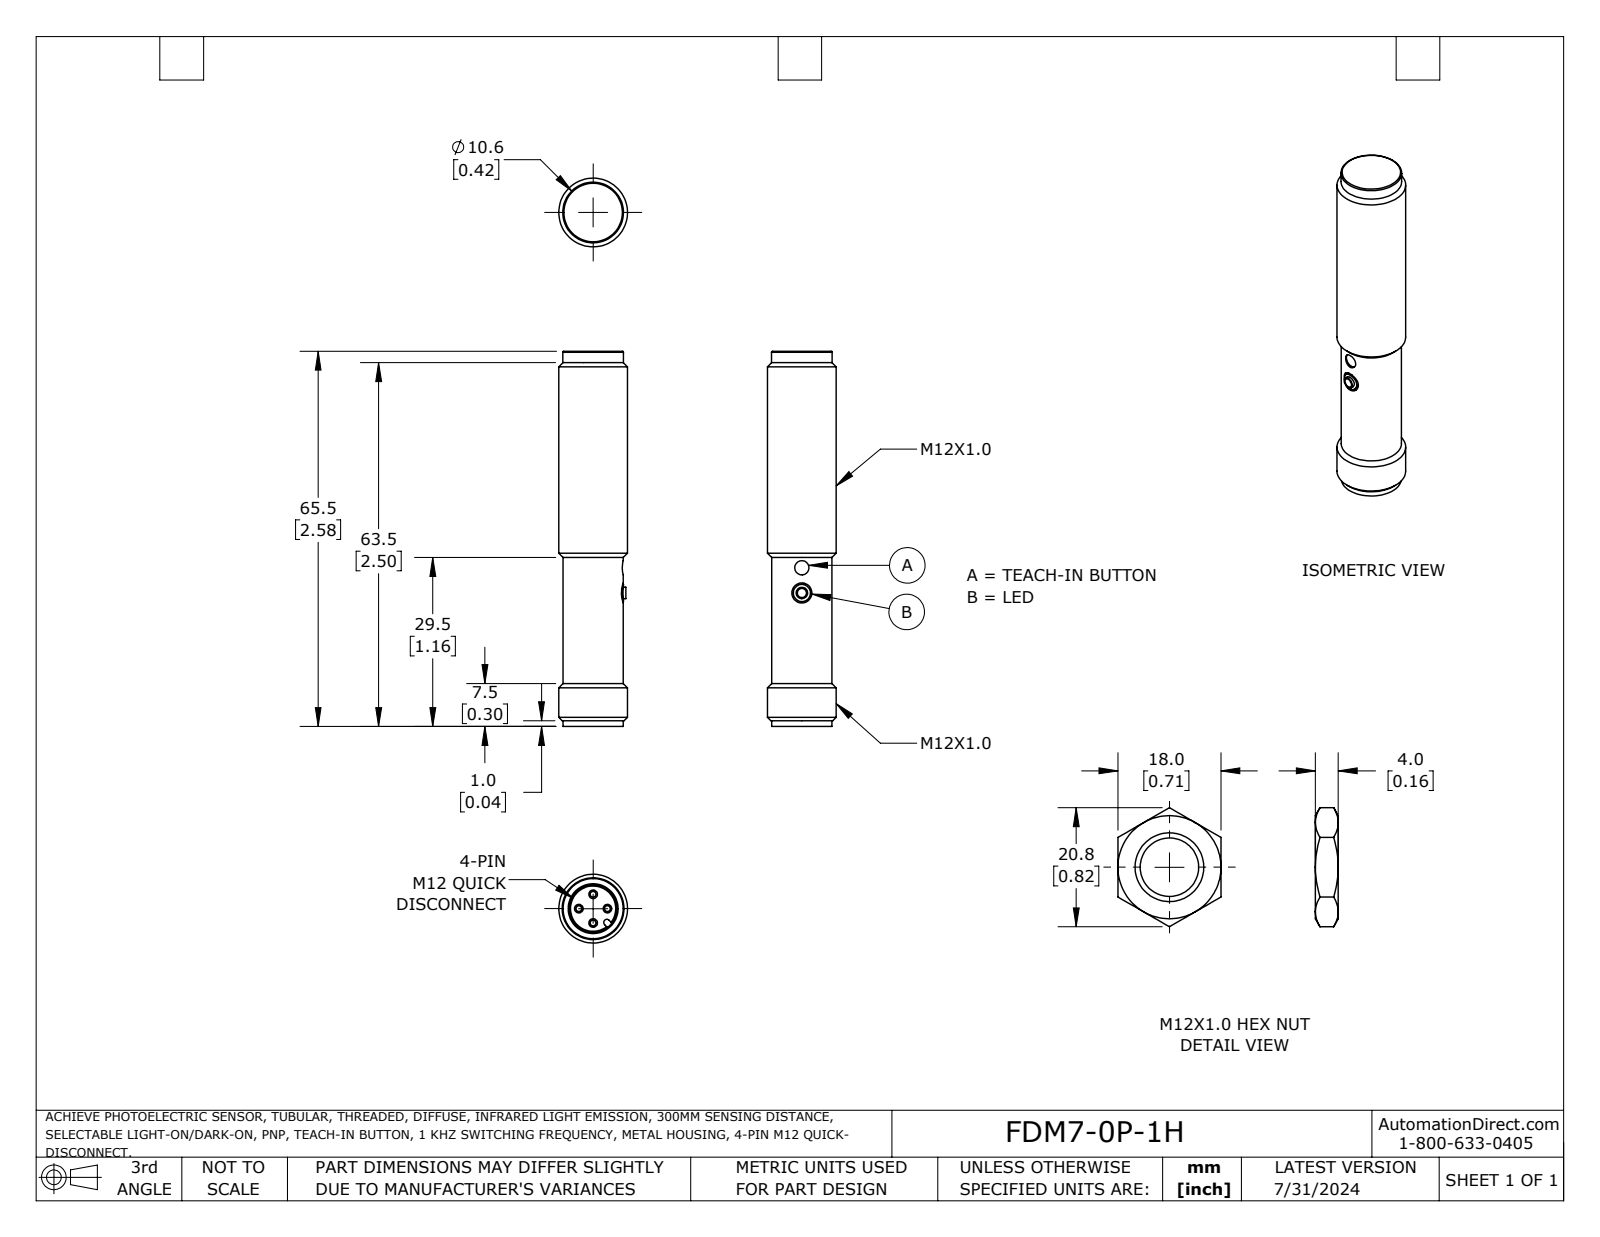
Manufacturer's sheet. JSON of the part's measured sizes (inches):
{"part_name": "DM3_1H_fig", "step_written_by": "SolidWorks 2023 (AUTOMOTIVE_DESIGN)", "units": "inches", "bodies": {"solids": 1, "faces": 43, "planar": 10, "cylindrical": 17, "other": 16}, "overall_size": [2.579, 0.472, 0.472], "volume_in3": 0.383, "surface_area_in2": 4.511, "round_holes": [[0.098, 1], [0.138, 1], [0.327, 1]], "round_bosses_or_shafts": [[0.039, 4], [0.472, 1], [0.417, 1], [0.413, 1], [0.118, 1], [0.079, 1]], "partial_cylinders_radius": [[0.022, 1], [0.193, 1]], "face_to_face_distances": [2.228, 0.35, 2.579, 0.043, 0.039, 0.311, 2.539, 0.02, 2.5, 2.461], "hole_center_spacings": [0.173]}
